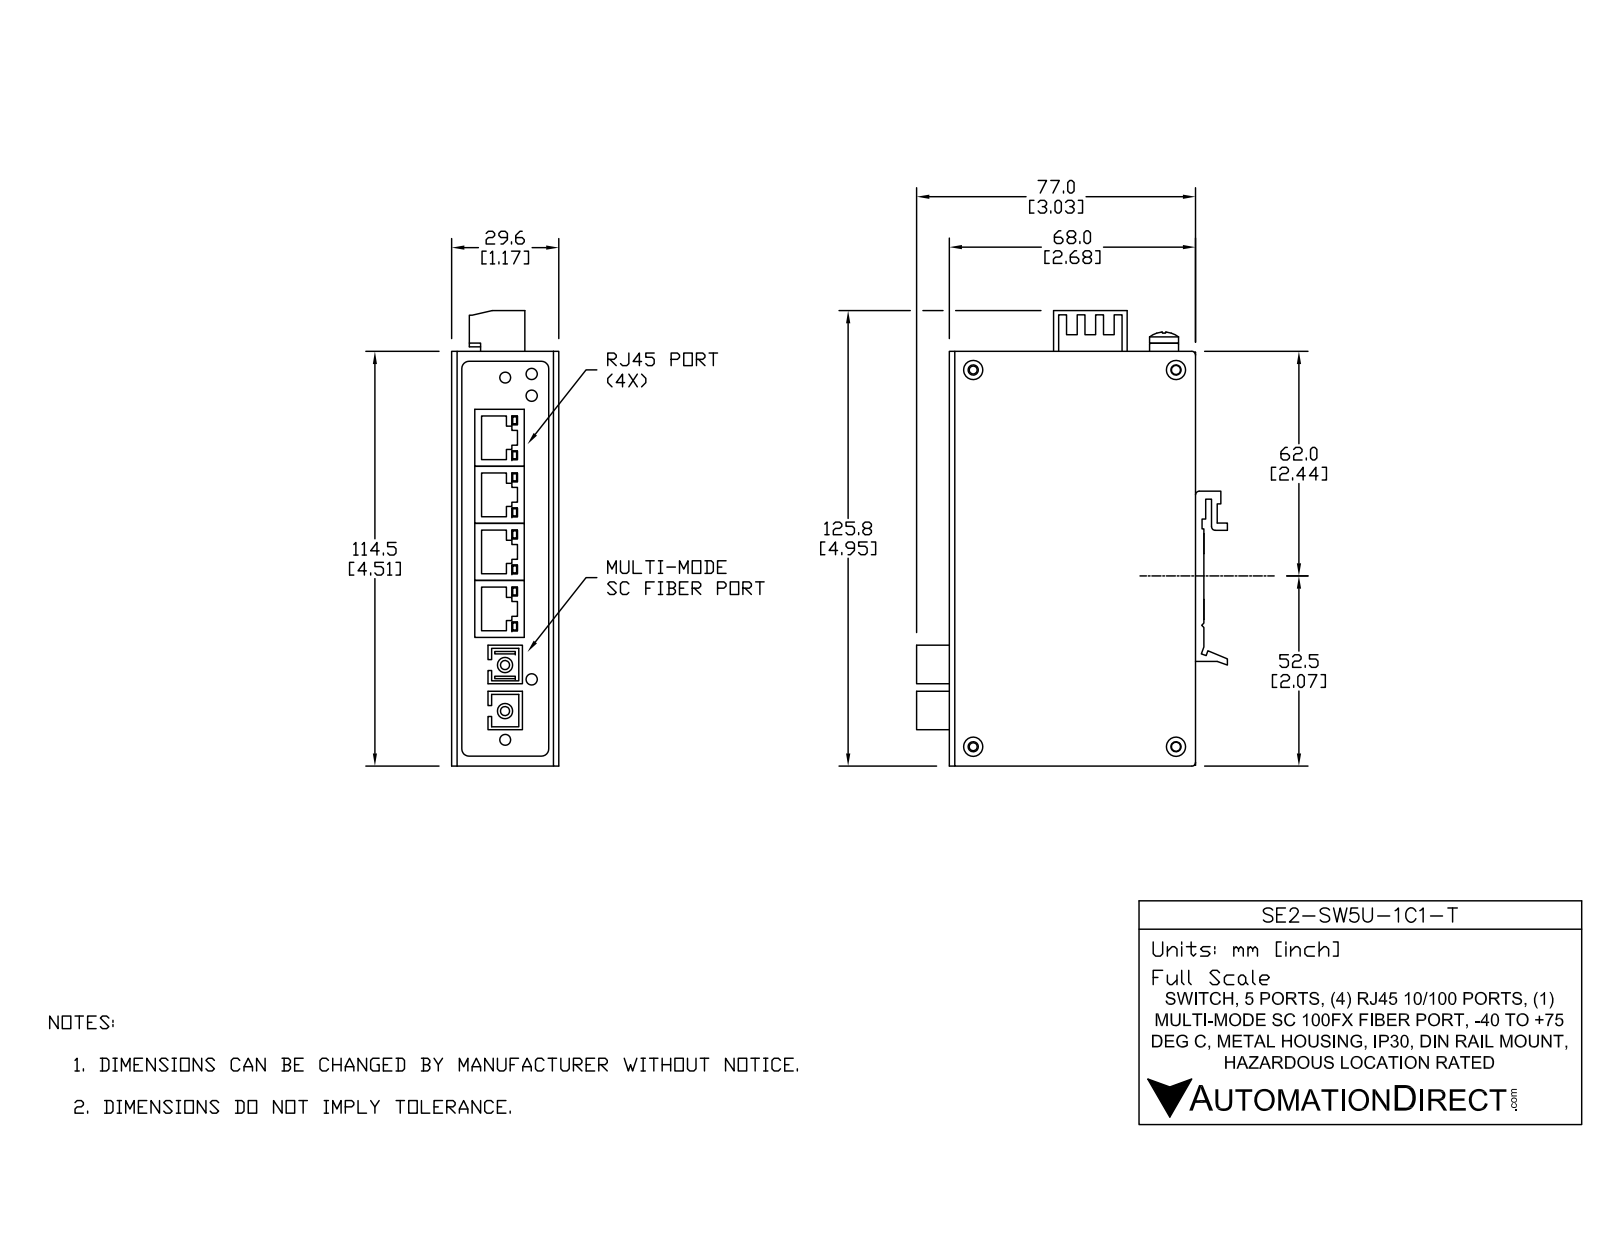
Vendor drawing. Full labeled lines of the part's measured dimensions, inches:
Part name (STEP PRODUCT): SE2-SW5U-1C1-T
STEP written by: SolidWorks 2017 (AUTOMOTIVE_DESIGN)
Units: inches
Bodies: 18 solids, 941 faces (644 planar, 250 cylindrical, 47 other)
Overall size (bounding box): 4.951 × 3.379 × 1.165
Volume: 2.914 in³ · Surface area: 132.9 in²
Round holes (diameter × count): ⌀0.11 ×4, ⌀0.15 ×4, ⌀0.122 ×3, ⌀0.099 ×2, ⌀0.118 ×2, ⌀0.134 ×2, ⌀0.155 ×1
Round bosses / shafts (diameter × count): ⌀0.142 ×4, ⌀0.217 ×2, ⌀0.197 ×2, ⌀0.165 ×2, ⌀0.118 ×2, ⌀0.315 ×1, ⌀0.157 ×1
Partial cylindrical surfaces — rounded edges, fillets, slot ends (radius × count): R0.024 ×96, R0.008 ×18, R0.026 ×16, R0.079 ×8, R0.118 ×8, R0.041 ×6, R0.039 ×5, R0.012 ×4
Main face-to-face distances: 0.039, 0.02, 1.087, 1.126, 0.079, 1.106, 1.067, 0.059, 1.047, 1.165
Hole centre spacings: 0.203, 0.4, 2.205, 4.094, 4.65, 0.197, 0.236, 0.29
